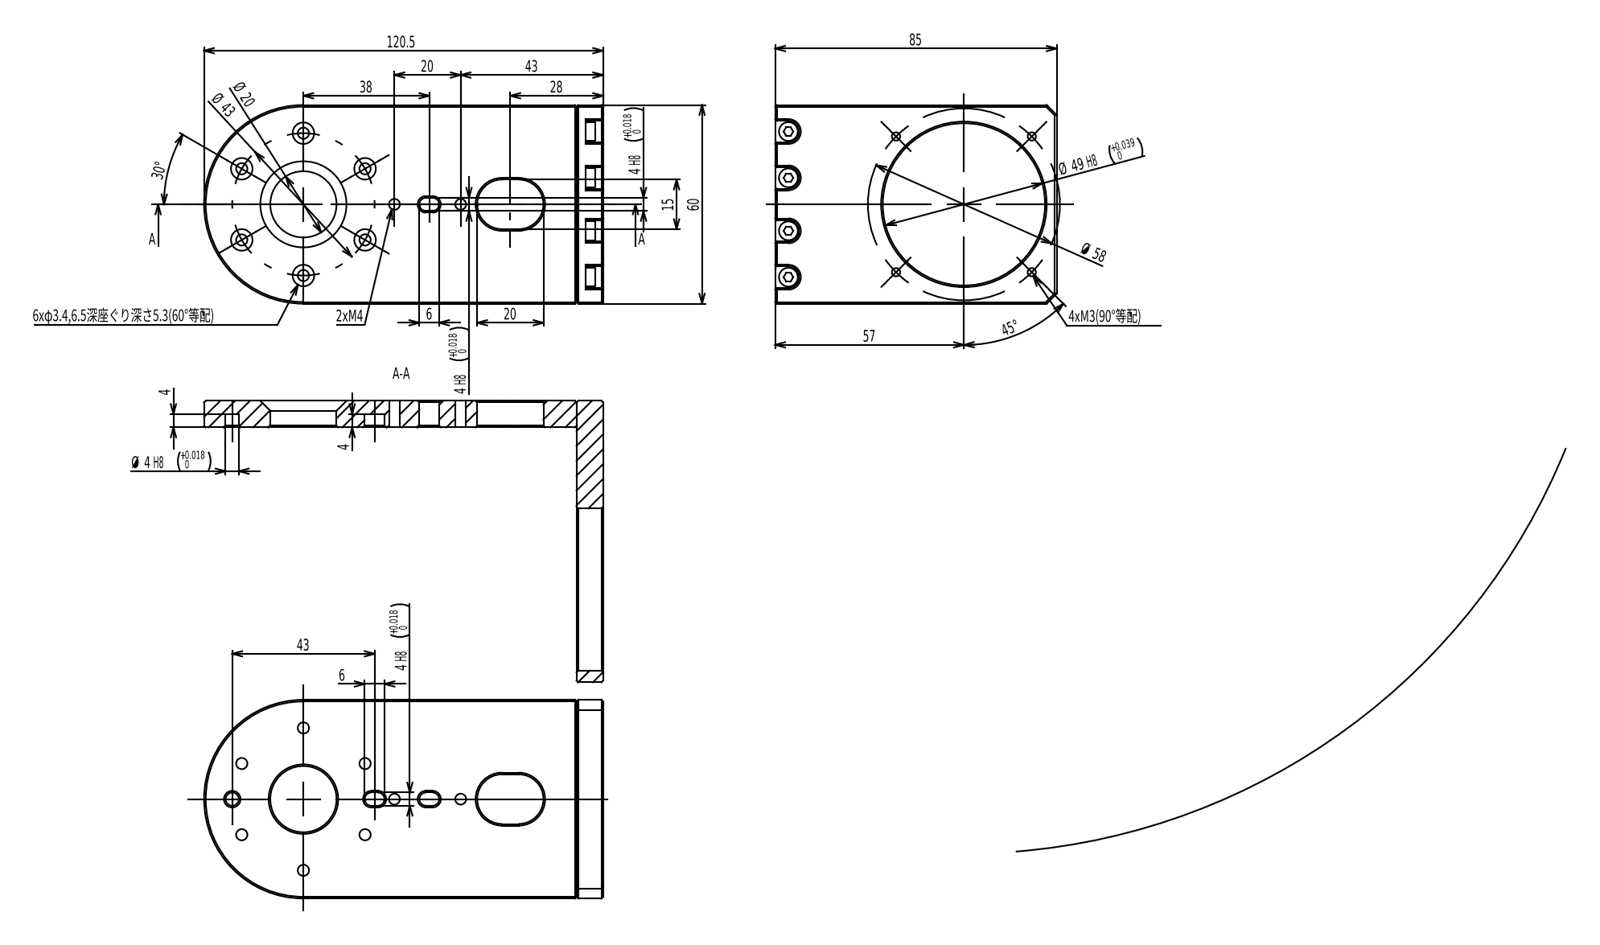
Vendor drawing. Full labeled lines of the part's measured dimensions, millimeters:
Part name (STEP PRODUCT): PDG60-5
STEP written by: SolidWorks 2020 (CONFIG_CONTROL_DESIGN)
Units: millimetres
Bodies: 6 solids, 283 faces (147 planar, 88 cylindrical, 48 other)
Overall size (bounding box): 120.49 × 85 × 60
Volume: 68 978 mm³ · Surface area: 26 992 mm²
Round holes (diameter × count): ⌀3.4 ×10, ⌀2.5 ×8, ⌀6.5 ×6, ⌀3.3 ×2, ⌀4 ×1, ⌀20 ×1, ⌀49 ×1
Round bosses / shafts (diameter × count): ⌀5.68 ×4, ⌀2.46 ×4
Partial cylindrical surfaces — rounded edges, fillets, slot ends (radius × count): R2 ×4, R3.25 ×4, R7.5 ×2, R30 ×1
Main face-to-face distances: 8, 60, 77, 85, 2.7, 5.3, 79.7, 47.36, 47.37, 4
Hole centre spacings: 21.5, 37.24, 41.01, 43, 11.13, 13.94, 14, 29
